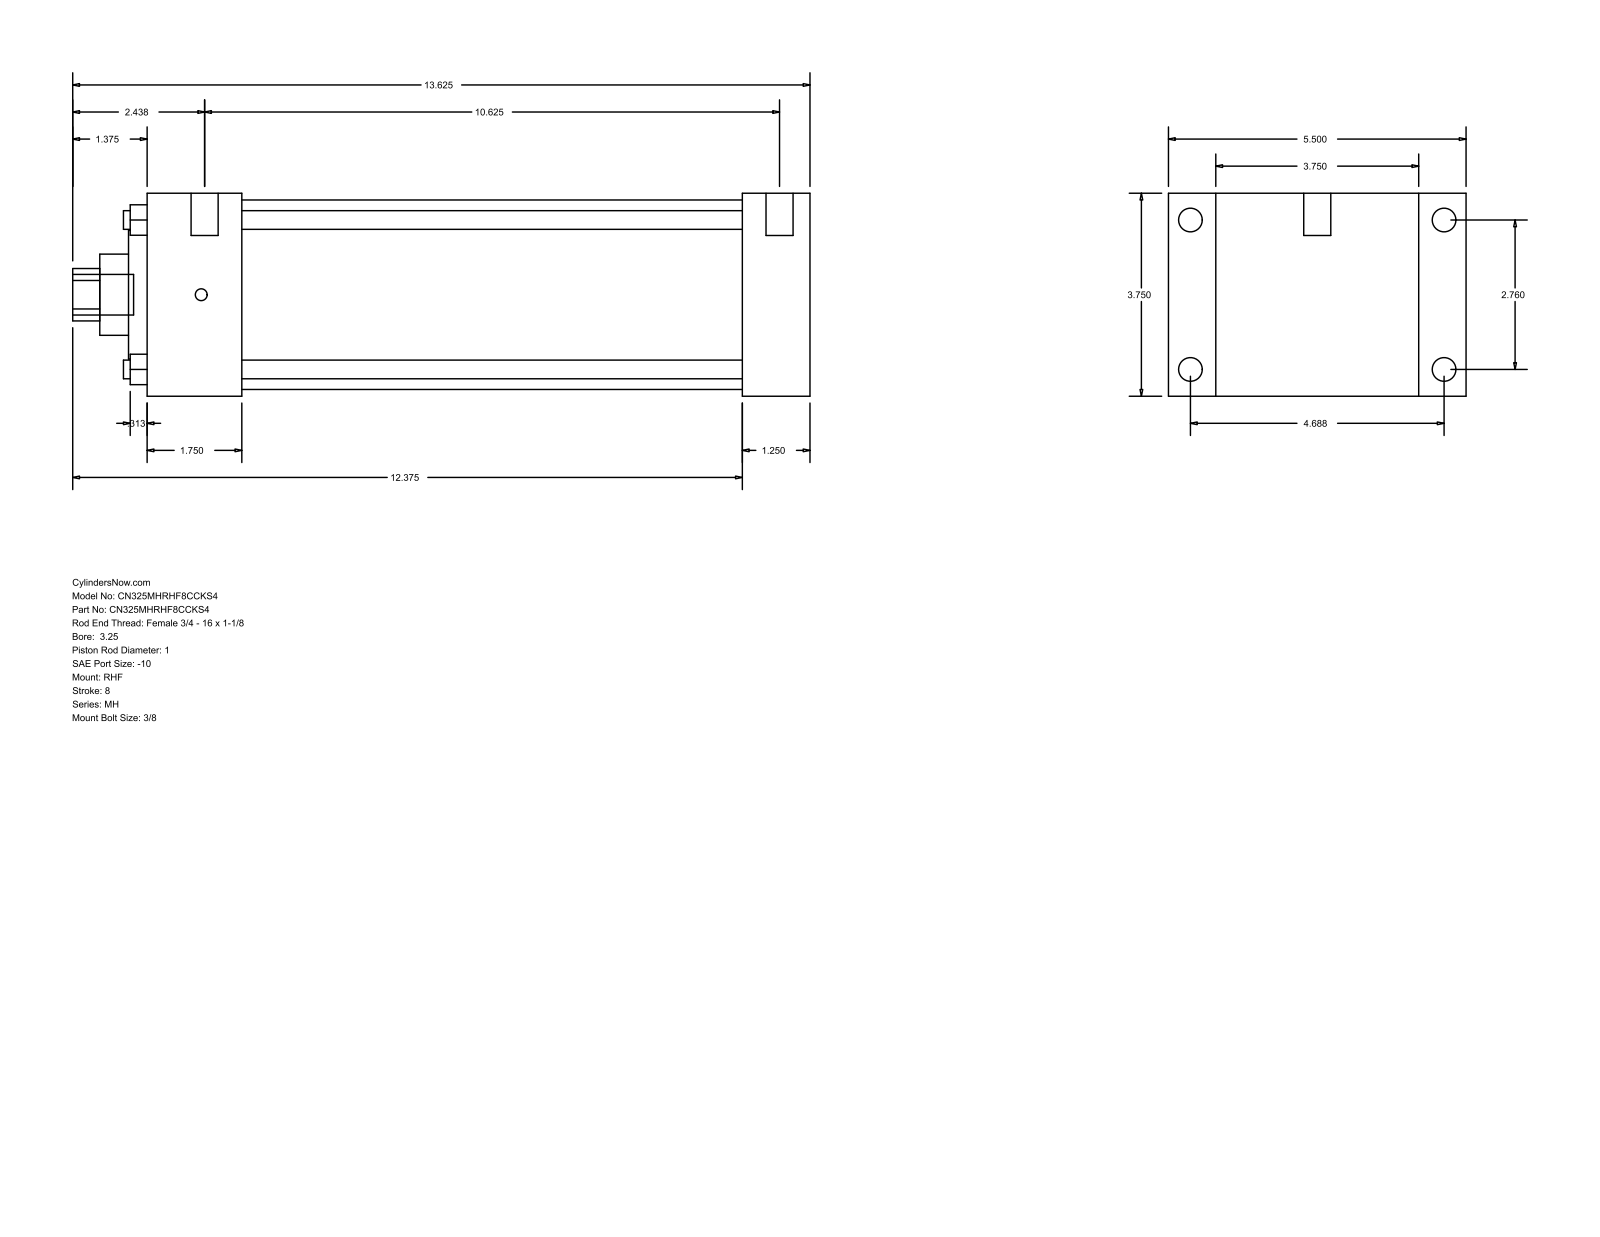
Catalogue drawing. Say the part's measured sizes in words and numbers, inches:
The part is named "MH_RHF__0325_1". Its 3-D file was written by "GSSL Pune (CONFIG_CONTROL_DESIGN)". It is 0 solids with 90 faces: 61 planar, 29 cylindrical and 0 other. Overall it measures 13.625 by 5.5 by 3.75 inches. Round holes: 4 of diameter 0.345, 1 of diameter 1, 1 of diameter 1.5, 1 of diameter 2.375, 1 of diameter 3.5. Round bosses or shafts: 4 of diameter 0.438, 4 of diameter 0.219, 2 of diameter 0.5, 1 of diameter 0.75. Partial cylindrical surfaces (rounded edges, fillets, slot ends): 1 of radius 0.484. The main face-to-face distances are 3.75, 1.25, 0.875, 4.625, 11, 12.25, 5.5, 1.75, 9.25, 10.5. The hole center spacings are 1.952, 2.76, 3.903.
